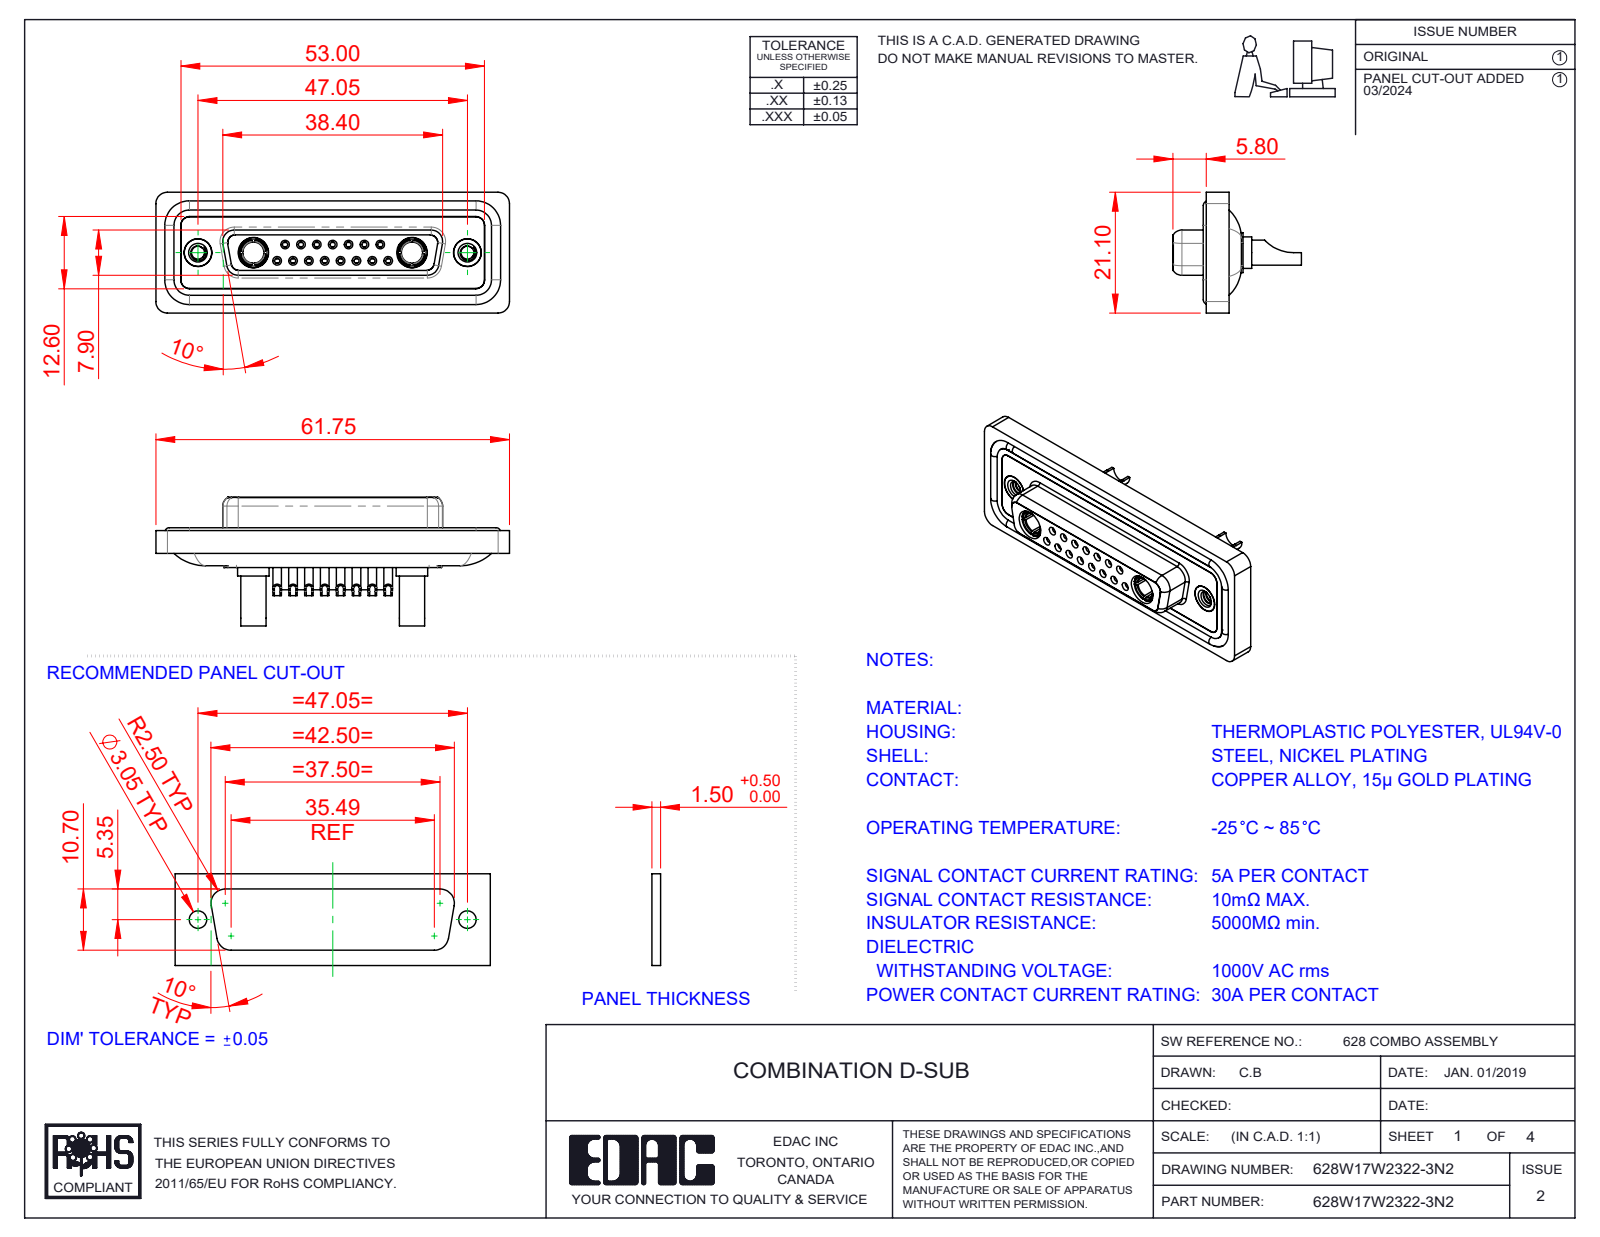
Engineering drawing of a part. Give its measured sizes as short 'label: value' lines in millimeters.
name: Power Socket_30A SC; 628Combo Housing_17W2; 628Combo Shell Rear_25 Contacts; 628Combo Threaded Rivet_2 (+5 more)
written by: SolidWorks 2023 (CONFIG_CONTROL_DESIGN)
unit: mm
bodies: 26 solids, 1371 faces (424 planar, 555 cylindrical, 392 other)
size: 61.75 × 22.45 × 21.1
volume: 8 403 mm³; area: 14 230 mm²
holes: 15× ⌀0.9, 15× ⌀1, 15× ⌀1.1, 15× ⌀1.5, 15× ⌀2, 8× ⌀1.6, 7× ⌀1.7, 4× ⌀4.85, 2× ⌀2.26, 2× ⌀3.5, 2× ⌀3.7, 2× ⌀4
bosses: 15× ⌀2.2, 11× ⌀1.6, 2× ⌀5.5, 2× ⌀5.2, 2× ⌀4.96, 2× ⌀4.95, 2× ⌀4.8, 2× ⌀4.75
rounds: 22× R1.5, 18× R2, 8× R1.35, 8× R1.6, 6× R1, 4× R0.25, 4× R0.5, 4× R0.6
face distances: 0.4, 1.8, 7.45, 5.65, 6.6, 0.5, 7.05, 1.6, 2.9, 1.1
hole spacings: 3.16, 2.77, 8.31, 5.54, 5.03, 5.04, 7.49, 11.08
